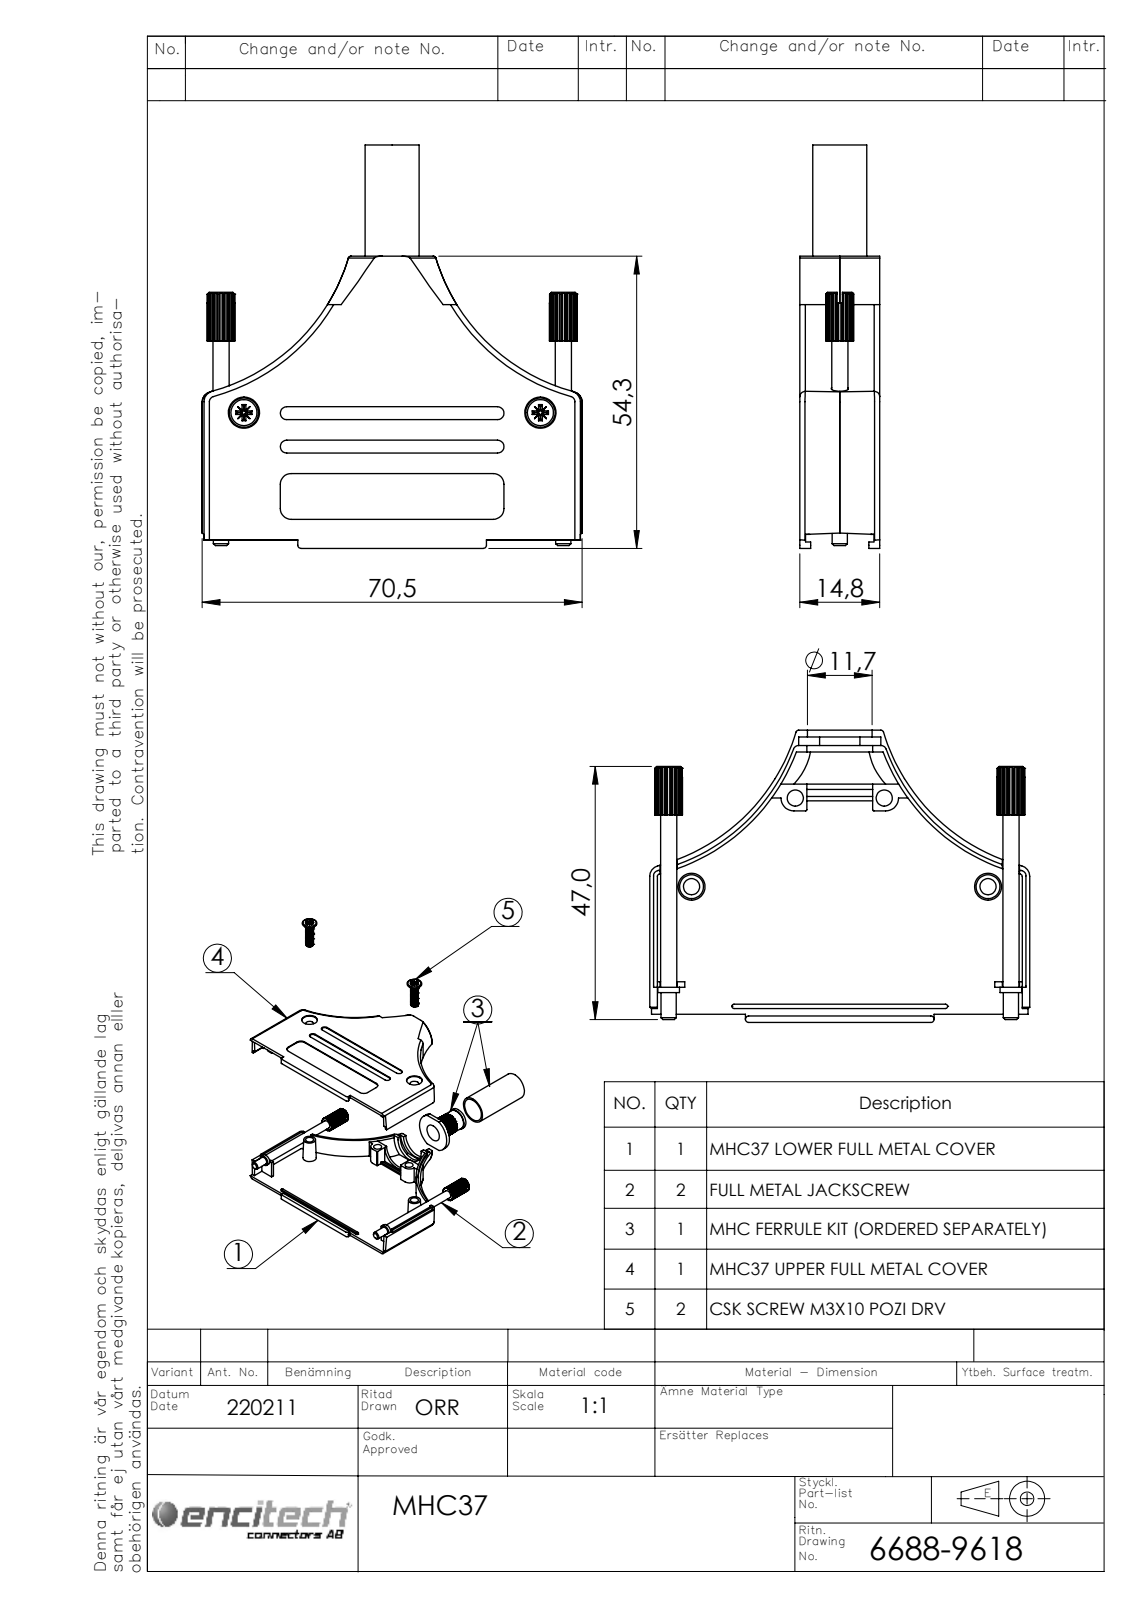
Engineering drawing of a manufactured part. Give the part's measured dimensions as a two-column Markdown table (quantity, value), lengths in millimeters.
| quantity | value |
| --- | --- |
| part name | 6855-0117-03; 6560-0135-04; 6826-0141-02; 6522-0110-12 (+3 more) |
| STEP written by | SolidWorks 2021 (AUTOMOTIVE_DESIGN) |
| units | millimeters |
| bodies | 8 solids, 1686 faces (381 planar, 433 cylindrical, 872 other) |
| overall size | 74.9 × 70.5 × 14.8 |
| volume | 10 286 mm³ |
| surface area | 20 564 mm² |
| round holes (diameter × count) | 3 × 4, 3.2 × 2, 4.5 × 2, 5.8 × 2, 3.3 × 1, 6.5 × 1, 8.8 × 1, 12 × 1, 12.2 × 1 |
| round bosses / shafts (diameter × count) | 4 × 2, 3 × 2, 2.9 × 2, 2.8 × 2, 10 × 1, 8 × 1, 7.5 × 1 |
| partial cylindrical surfaces (radius × count) | 1 × 12, 0.1 × 8, 36.71 × 7, 0.2 × 4, 1.2 × 4, 2 × 4, 0.25 × 3, 0.4 × 2 |
| main face-to-face distances | 13.75, 1.05, 12.7, 14.8, 14.5, 0.75, 13.45, 14.2, 6.35, 7.1 |
| hole center spacings | 25.32, 31.75, 39.35, 16.5, 55, 63.5 |
